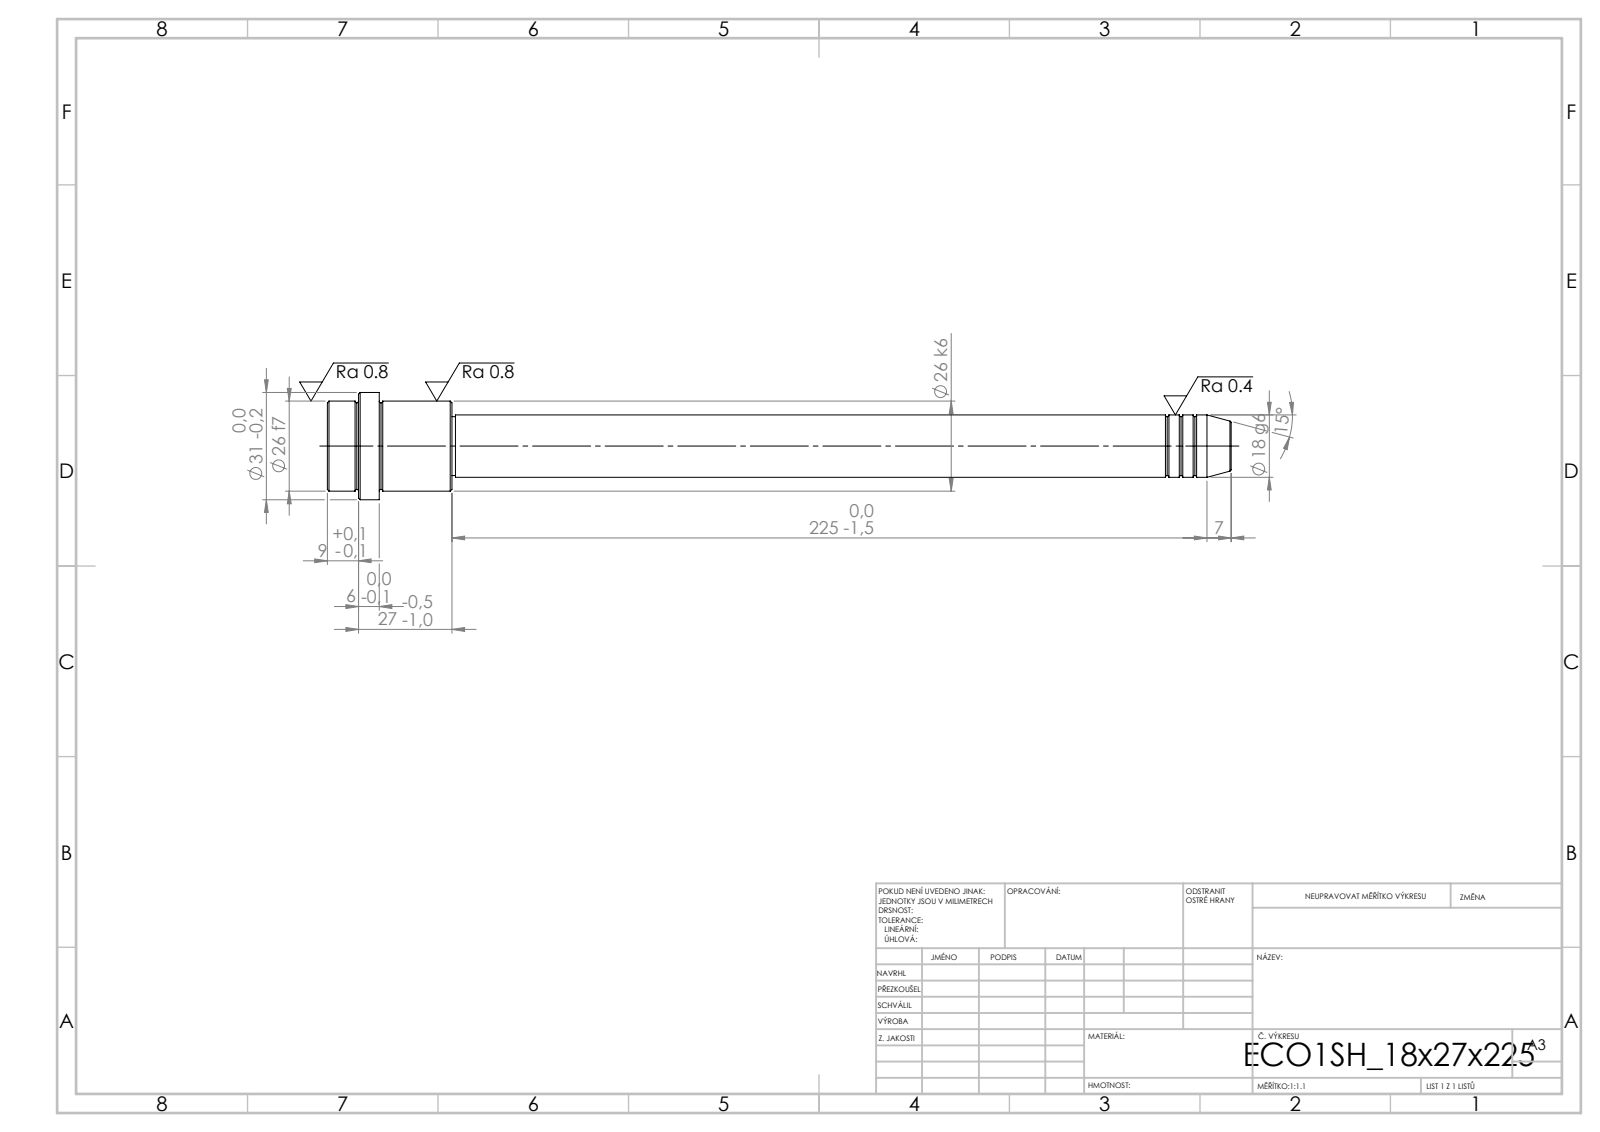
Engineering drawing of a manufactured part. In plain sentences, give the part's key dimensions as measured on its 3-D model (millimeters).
Its 3-D file was written by "SolidWorks 2019 (CONFIG_CONTROL_DESIGN)". It is 1 solid with 52 faces: 6 planar, 16 cylindrical and 30 other. Overall it measures 261 by 31 by 31 millimeters. Its volume is 77 177 cubic millimeters and its surface area 17 288 square millimeters. Round bosses or shafts: 1 of diameter 31, 1 of diameter 26, 1 of diameter 18, 1 of diameter 17. The main face-to-face distances are 36, 21, 15, 27, 6, 9, 225, 246, 252, 261.
